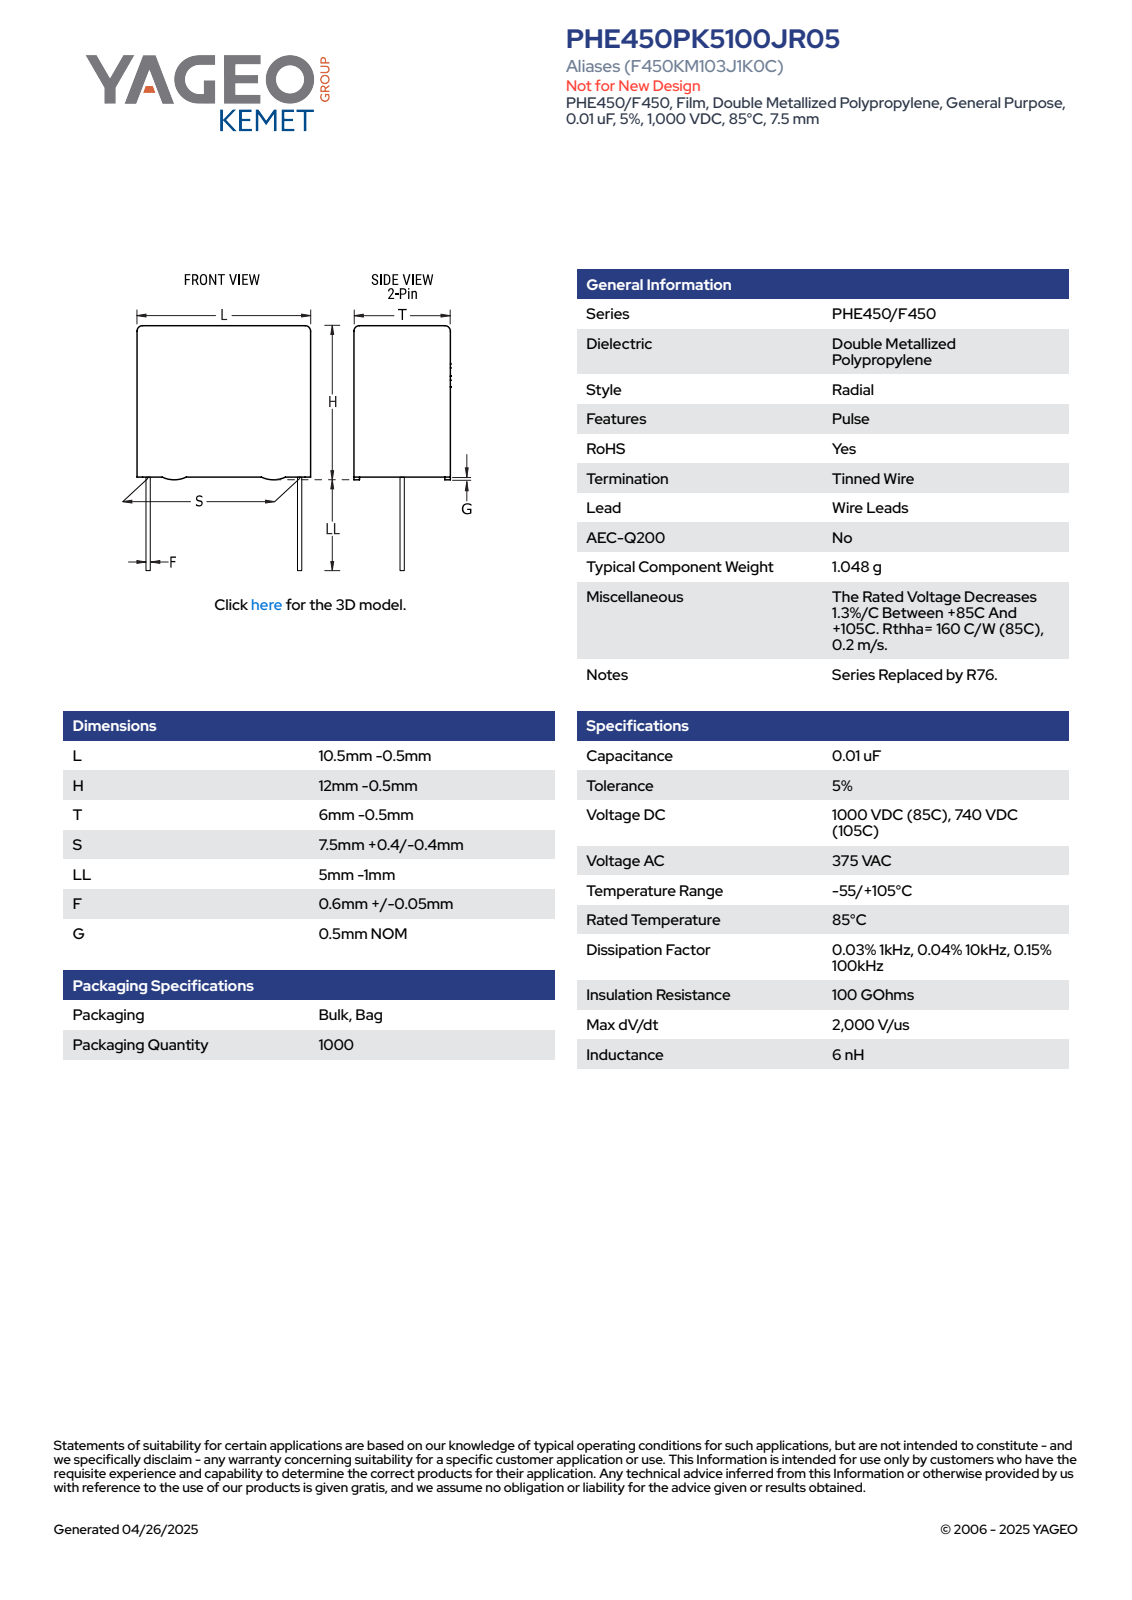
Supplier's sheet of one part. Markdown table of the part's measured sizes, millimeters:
| quantity | value |
| --- | --- |
| part name | CFR_RBG_10.5X12X6_L10H11.5T5.5S7.5LL4F0.65G0.5 |
| STEP written by | SolidWorks 2020 (AUTOMOTIVE_DESIGN) |
| units | millimeters |
| bodies | 4 solids, 89 faces (81 planar, 8 cylindrical, 0 other) |
| overall size | 15.5 × 10 × 5.5 |
| volume | 607 mm³ |
| surface area | 481 mm² |
| round bosses / shafts (diameter × count) | 0.65 × 2 |
| partial cylindrical surfaces (radius × count) | 0.5 × 4 |
| main face-to-face distances | 5.5, 10, 11, 5.19, 0.31, 0.5, 11.5, 4.88, 4, 4.5 |
